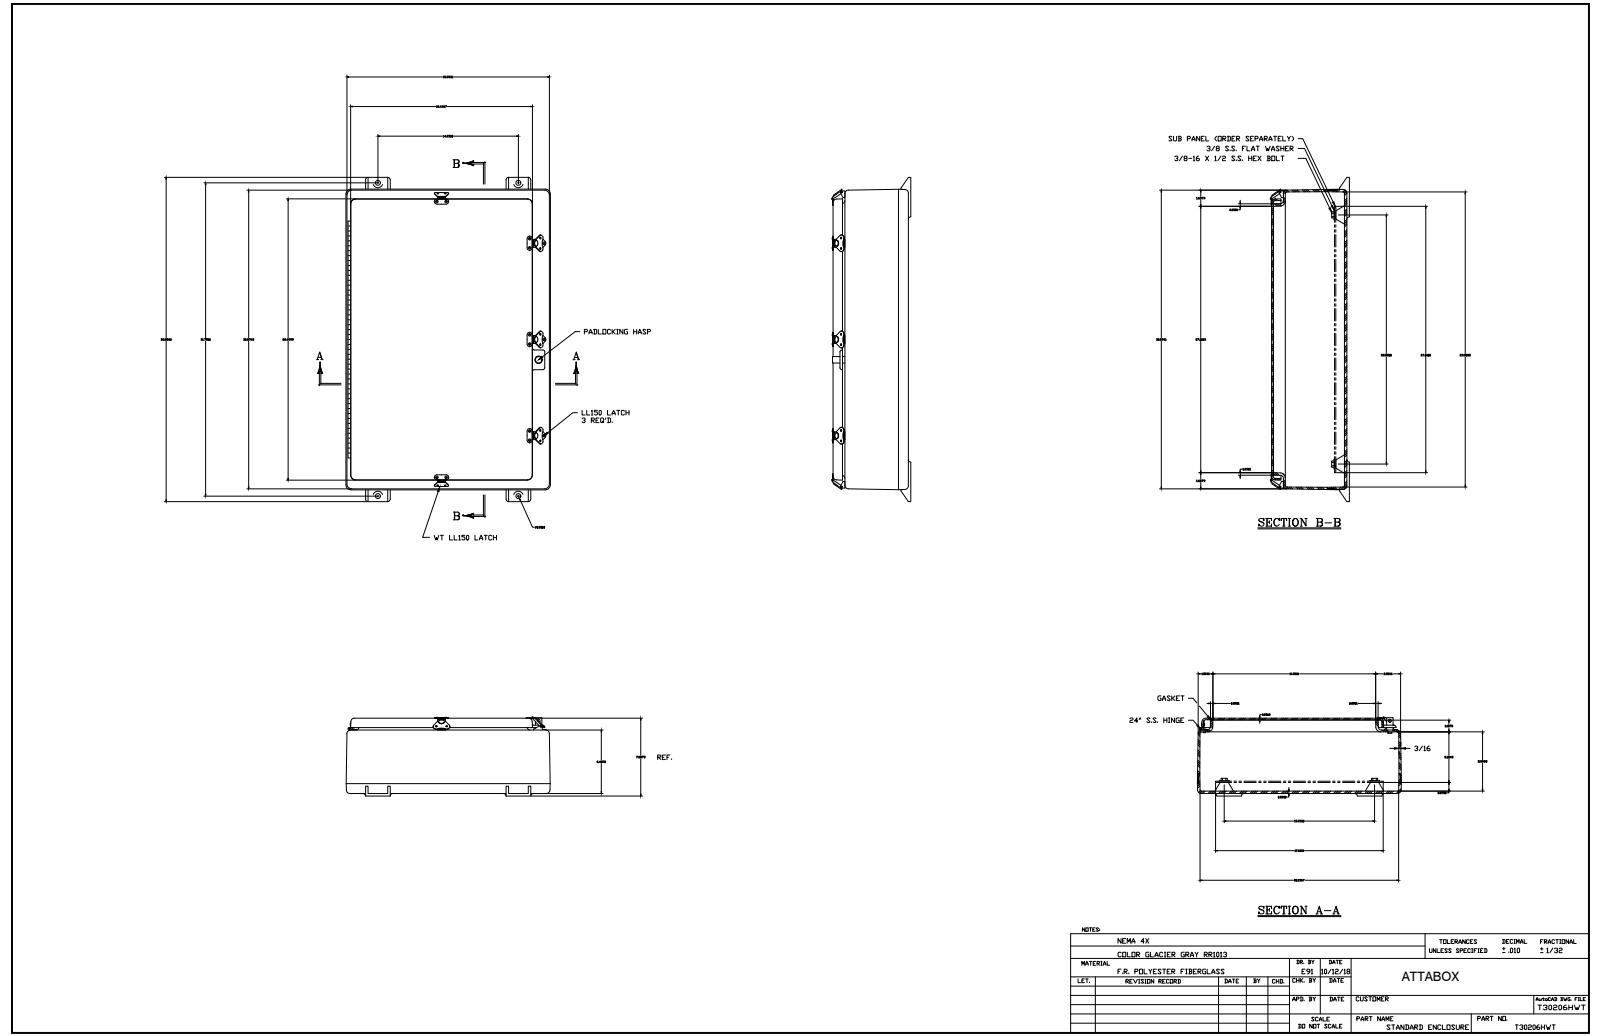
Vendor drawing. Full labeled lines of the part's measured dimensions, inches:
Part name (STEP PRODUCT): T30206HWT
STEP written by: SolidWorks 2018 (AUTOMOTIVE_DESIGN)
Units: inches
Bodies: 63 solids, 1702 faces (646 planar, 690 cylindrical, 366 other)
Overall size (bounding box): 32.844 × 20.75 × 8.241
Volume: 441 in³ · Surface area: 4 670 in²
Round holes (diameter × count): ⌀0.13 ×36, ⌀0.063 ×20, ⌀0.138 ×10, ⌀0.187 ×10, ⌀0.065 ×4, ⌀0.065 ×4, ⌀0.563 ×4, ⌀0.135 ×3, ⌀0.156 ×3, ⌀0.51 ×2, ⌀0.51 ×2, ⌀0.125 ×1
Round bosses / shafts (diameter × count): ⌀0.14 ×20, ⌀0.297 ×8, ⌀0.5 ×5, ⌀0.2 ×3, ⌀0.135 ×3, ⌀0.25 ×1, ⌀0.201 ×1
Partial cylindrical surfaces — rounded edges, fillets, slot ends (radius × count): R0.01 ×127, R0.375 ×21, R0.03 ×20, R0.25 ×20, R0.187 ×15, R0.188 ×14, R0.313 ×13, R0.5 ×12
Main face-to-face distances: 0.25, 0.156, 0.187, 7.469, 7.219, 7.375, 7.625, 0.063, 0.125, 1.187
Hole centre spacings: 9.75, 0.858, 1.542, 7.5, 15.5, 19.5, 1, 3.211
